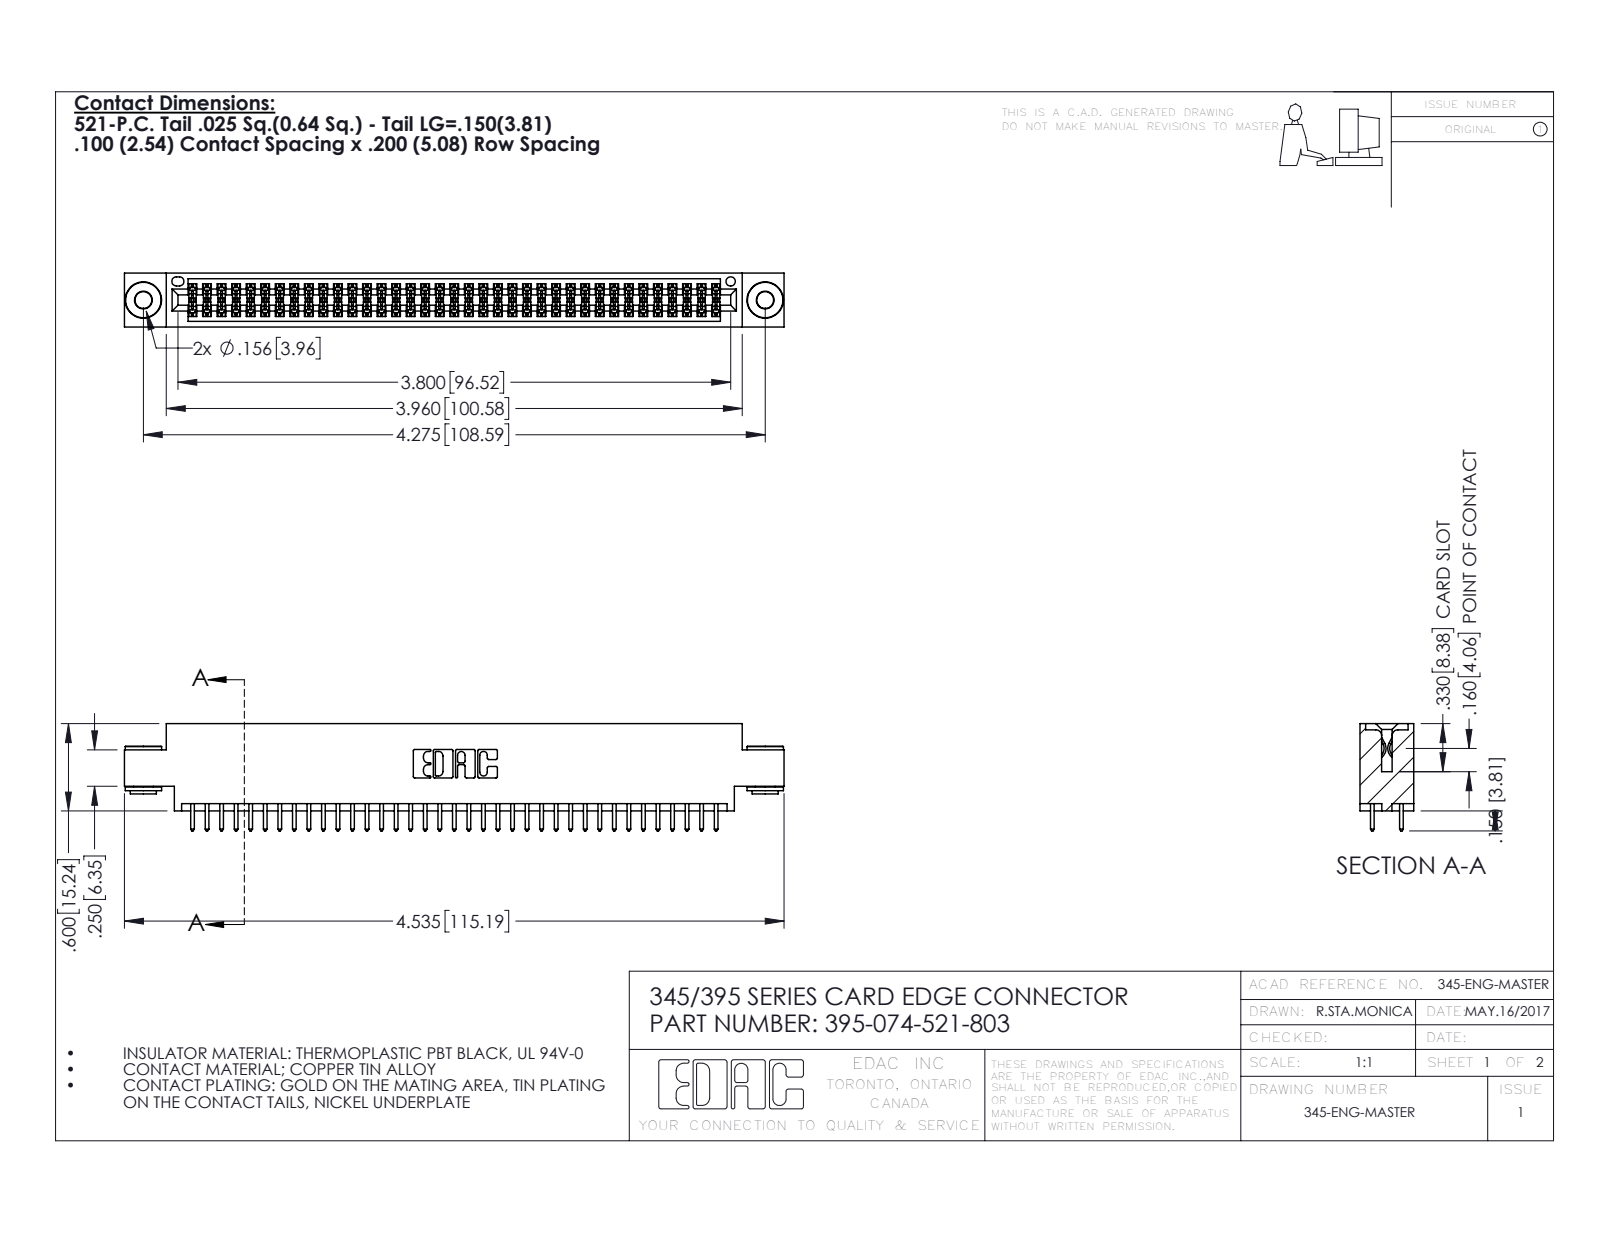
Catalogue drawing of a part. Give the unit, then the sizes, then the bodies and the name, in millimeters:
Units: millimetres
Overall size (bounding box): 115.2 × 18.7 × 9.4
Round holes (diameter × count): ⌀2.9 ×2, ⌀4 ×2, ⌀1.6 ×1
Round bosses / shafts (diameter × count): ⌀6.4 ×2, ⌀4.6 ×2, ⌀3.5 ×2
Partial cylindrical surfaces — rounded edges, fillets, slot ends (radius × count): R0.2 ×111, R0.3 ×74, R0.3 ×22, R0.2 ×6, R0.8 ×6, R0.7 ×3, R0.4 ×2, R0.5 ×2
Main face-to-face distances: 1.8, 7.6, 9.4, 5.1, 2.5, 6.9, 0.6, 5.7, 4.4, 3.8
Hole centre spacings: 6.9, 102.6, 108.6
Volume: 11 000 mm³ · Surface area: 16 340 mm²
Bodies: 77 solids, 3868 faces (2536 planar, 1324 cylindrical, 8 other)
Part name (STEP PRODUCT): 395-074-521-803; 345 Part_0.170 Offset - 0.156 Dia-TH; 345-292-001_345-293-121; 345-250-002_345-250-002-102
STEP written by: SolidWorks 2016 (CONFIG_CONTROL_DESIGN)
